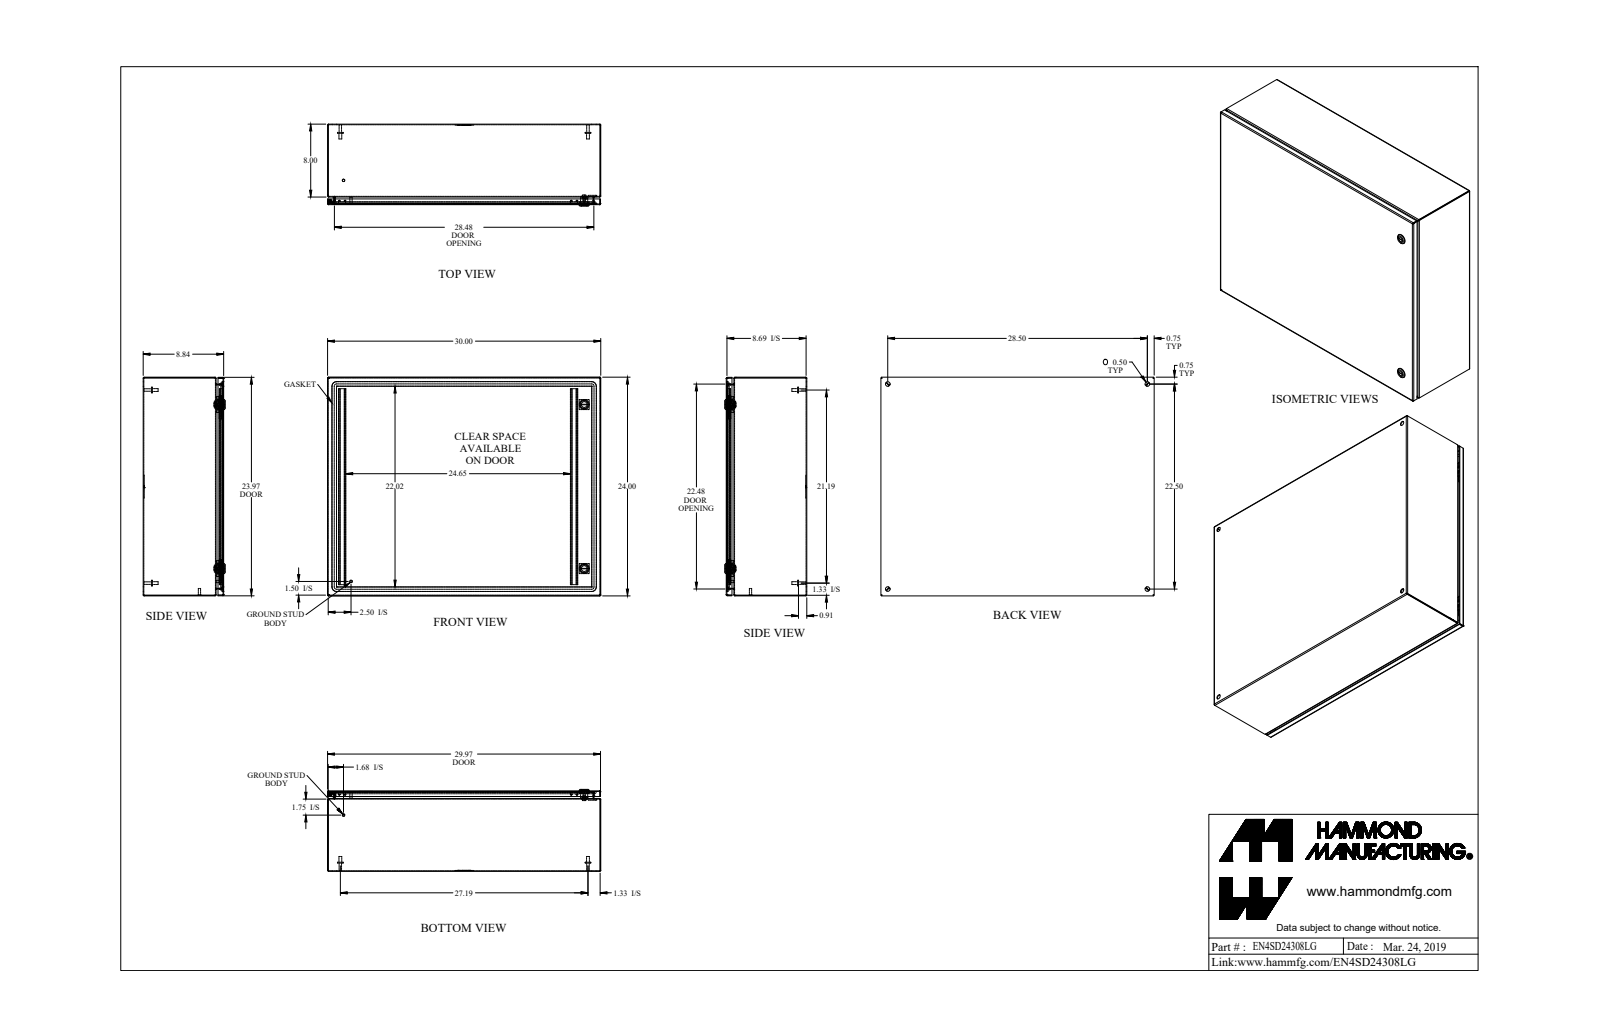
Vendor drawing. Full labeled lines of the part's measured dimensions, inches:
Part name (STEP PRODUCT): EN4SD24308LG_Default
STEP written by: SolidWorks 2019 (CONFIG_CONTROL_DESIGN)
Units: inches
Bodies: 27 solids, 783 faces (386 planar, 257 cylindrical, 140 other)
Overall size (bounding box): 30 × 24 × 8.997
Volume: 194.3 in³ · Surface area: 5 429 in²
Round holes (diameter × count): ⌀0.5 ×4, ⌀0.232 ×2, ⌀0.625 ×2, ⌀0.785 ×2, ⌀0.172 ×1, ⌀0.24 ×1, ⌀0.242 ×1
Round bosses / shafts (diameter × count): ⌀0.625 ×4, ⌀0.313 ×4, ⌀0.27 ×4, ⌀1.1 ×2, ⌀0.525 ×2, ⌀0.281 ×2, ⌀0.25 ×2, ⌀0.455 ×1
Partial cylindrical surfaces — rounded edges, fillets, slot ends (radius × count): R0.036 ×20, R0.108 ×20, R0.043 ×12, R0.081 ×12, R0.382 ×12, R19.003 ×8, R0.006 ×4, R0.062 ×4
Main face-to-face distances: 0.072, 8.765, 8.693, 8.837, 23.928, 29.928, 23.856, 24, 29.856, 30
Hole centre spacings: 22.5, 27.519, 28.5, 36.311, 2.493, 2.494, 17.999, 20.277
